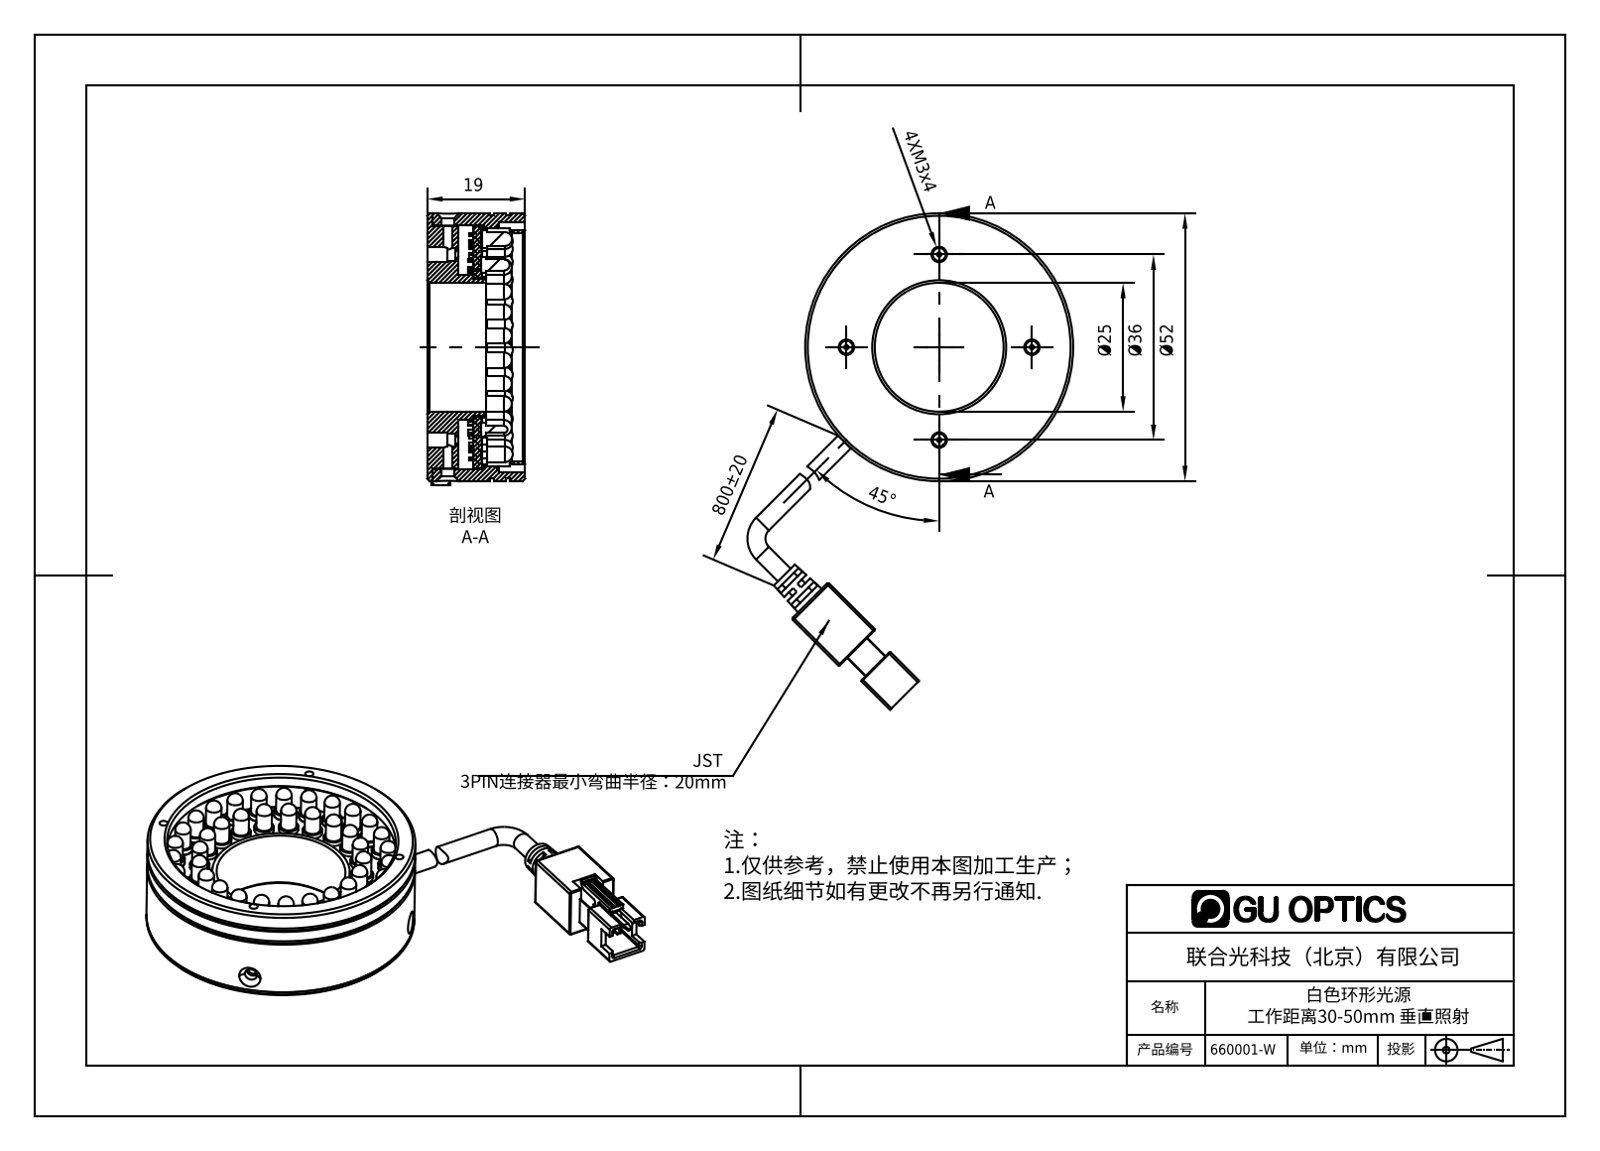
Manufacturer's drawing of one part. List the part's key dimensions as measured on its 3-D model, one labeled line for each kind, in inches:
Part name (STEP PRODUCT): 660001-W
STEP written by: SolidWorks 2016 (AUTOMOTIVE_DESIGN)
Units: inches
Bodies: 53 solids, 1320 faces (770 planar, 437 cylindrical, 113 other)
Overall size (bounding box): 3.794 × 2.489 × 0.841
Volume: 1.296 in³ · Surface area: 33.42 in²
Round holes (diameter × count): ⌀0.15 ×48, ⌀0.063 ×6, ⌀0.098 ×4, ⌀0.118 ×4, ⌀0.094 ×2, ⌀0.984 ×1, ⌀1.063 ×1, ⌀1.748 ×1, ⌀1.819 ×1, ⌀1.858 ×1
Round bosses / shafts (diameter × count): ⌀0.118 ×48, ⌀0.138 ×2, ⌀2.047 ×1, ⌀2.008 ×1, ⌀1.854 ×1, ⌀1.85 ×1, ⌀1.102 ×1, ⌀1.051 ×1
Partial cylindrical surfaces — rounded edges, fillets, slot ends (radius × count): R0.004 ×15, R0.008 ×13, R0.016 ×12, R0.012 ×1, R0.027 ×1, R0.055 ×1, R0.069 ×1, R0.315 ×1
Main face-to-face distances: 0.118, 0.039, 0.354, 0.236, 0.197, 0.181, 0.063, 0.417, 0.315, 0.394
Hole centre spacings: 0.63, 0.188, 0.985, 1.256, 0.371, 0.546, 1.091, 0.71
